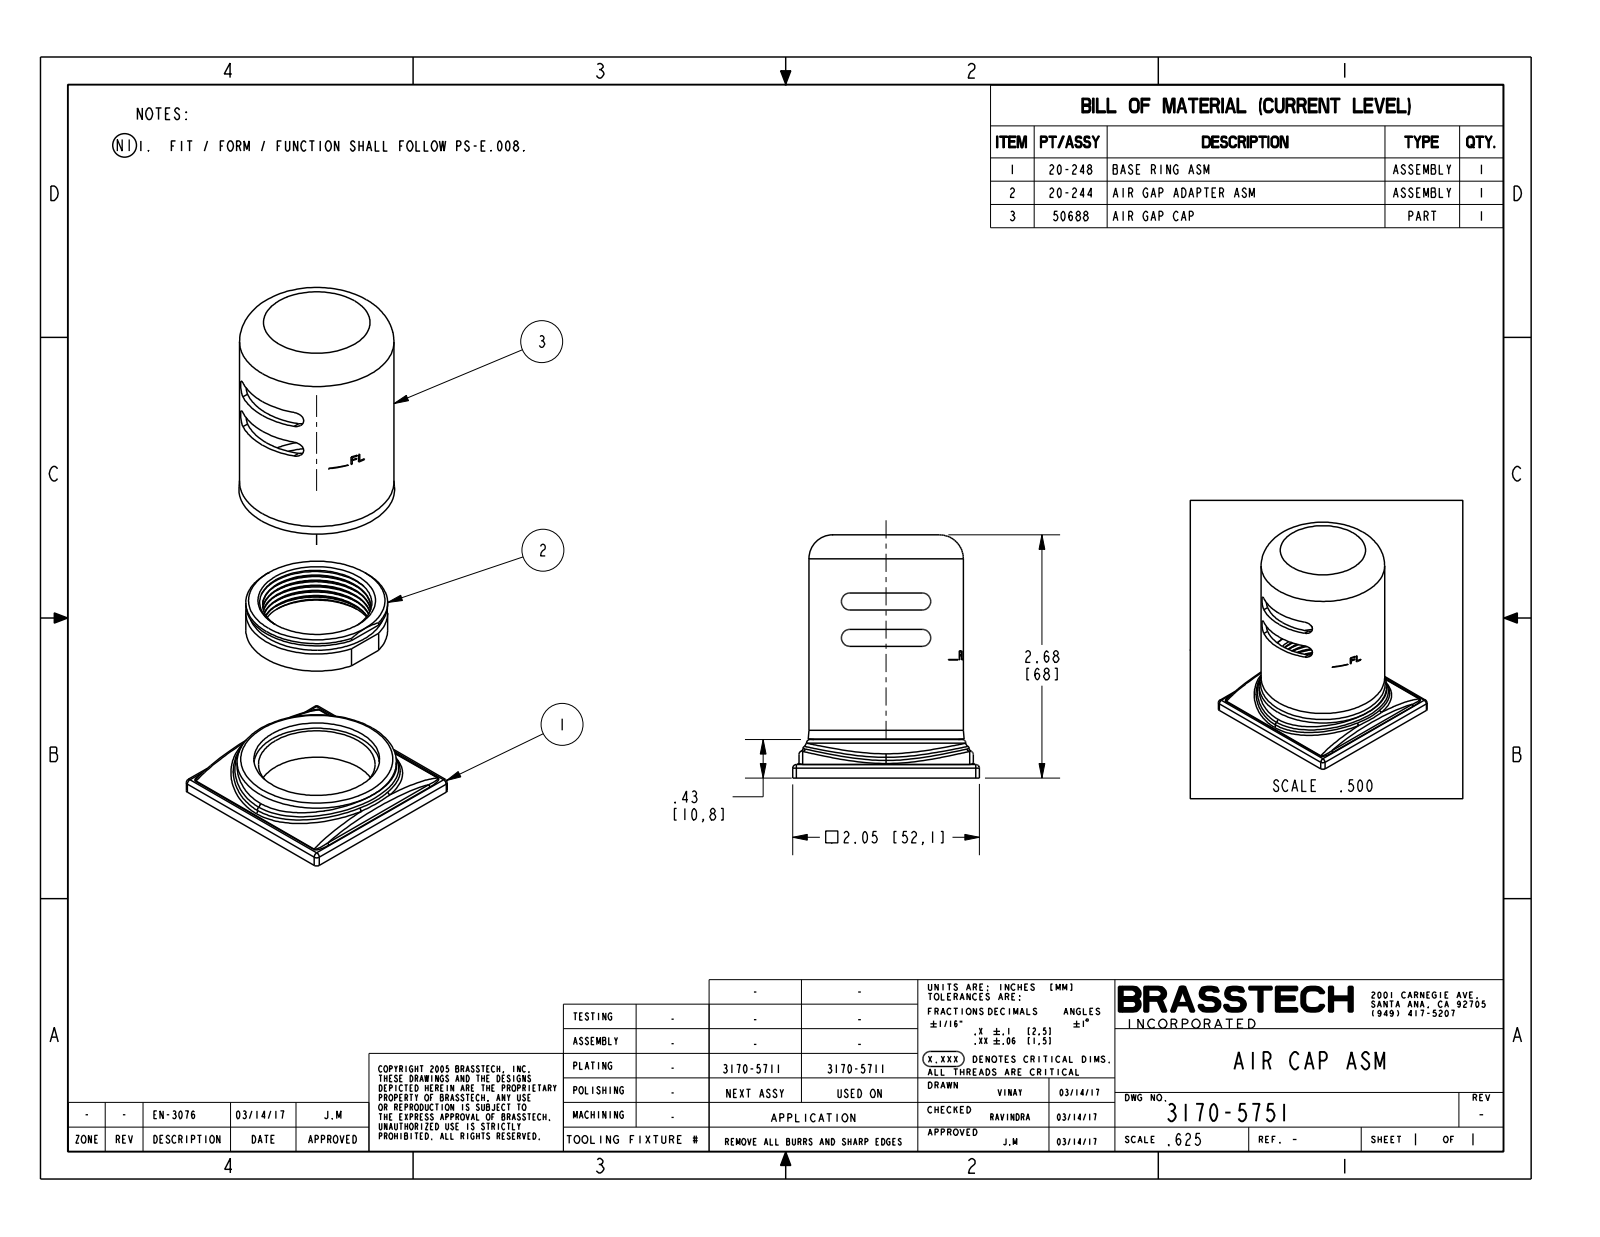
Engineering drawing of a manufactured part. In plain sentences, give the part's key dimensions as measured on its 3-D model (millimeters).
The part is named "12702; 12736; 91227; 20-244_ASM (+2 more)". Its 3-D file was written by "PRO/ENGINEER BY PARAMETRIC TECHNOLOGY CORPORATION, 2013150 (CONFIG_CONTROL_DESIGN)". It is 4 solids with 279 faces: 64 planar, 76 cylindrical and 139 other. Overall it measures 66.4 by 52.1 by 52.1 millimeters. Its volume is 23 120 cubic millimeters and its surface area 49 470 square millimeters. Round holes: 1 of diameter 30.2, 1 of diameter 32.3, 1 of diameter 35.1, 1 of diameter 40. Round bosses or shafts: 1 of diameter 44.5, 1 of diameter 41.5, 1 of diameter 39.4, 1 of diameter 35.3, 1 of diameter 34.5. Partial cylindrical surfaces (rounded edges, fillets, slot ends): 8 of radius 1, 4 of radius 0.5, 4 of radius 2, 4 of radius 2.5, 4 of radius 5.1, 1 of radius 20.5. The main face-to-face distances are 66.4, 10.8, 55.6, 65.7, 54.9, 0.8, 52.1, 2.2, 8.6, 63.5.
